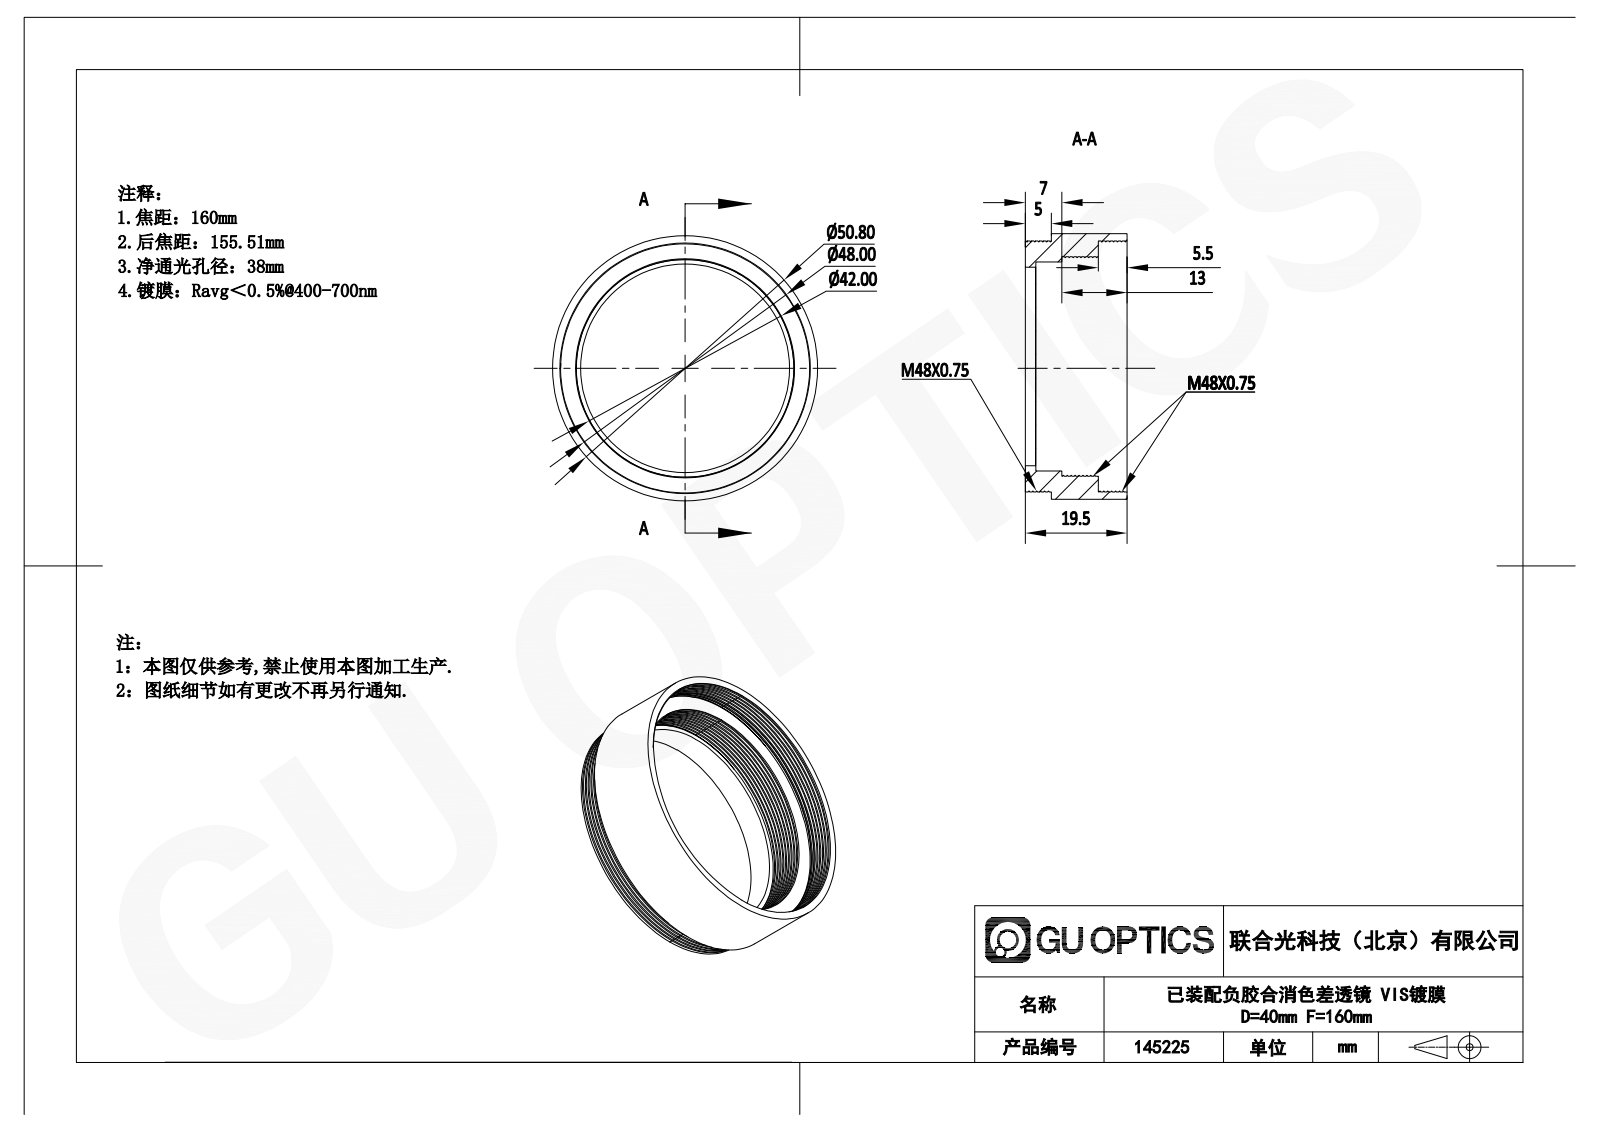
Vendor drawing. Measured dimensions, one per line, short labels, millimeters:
name: APD-ML40-160-VIS-A
written by: SolidWorks 2023 (CONFIG_CONTROL_DESIGN)
unit: mm
bodies: 1 solid, 81 faces (11 planar, 60 cylindrical, 10 other)
size: 50.8 × 50.8 × 19.5
volume: 10 286 mm³; area: 10 390 mm²
holes: 1× ⌀38, 1× ⌀40, 1× ⌀42, 1× ⌀48
bosses: 1× ⌀50.8
face distances: 2, 2.01, 14, 12, 11.99, 5, 7, 19.5, 17.5, 17.49
